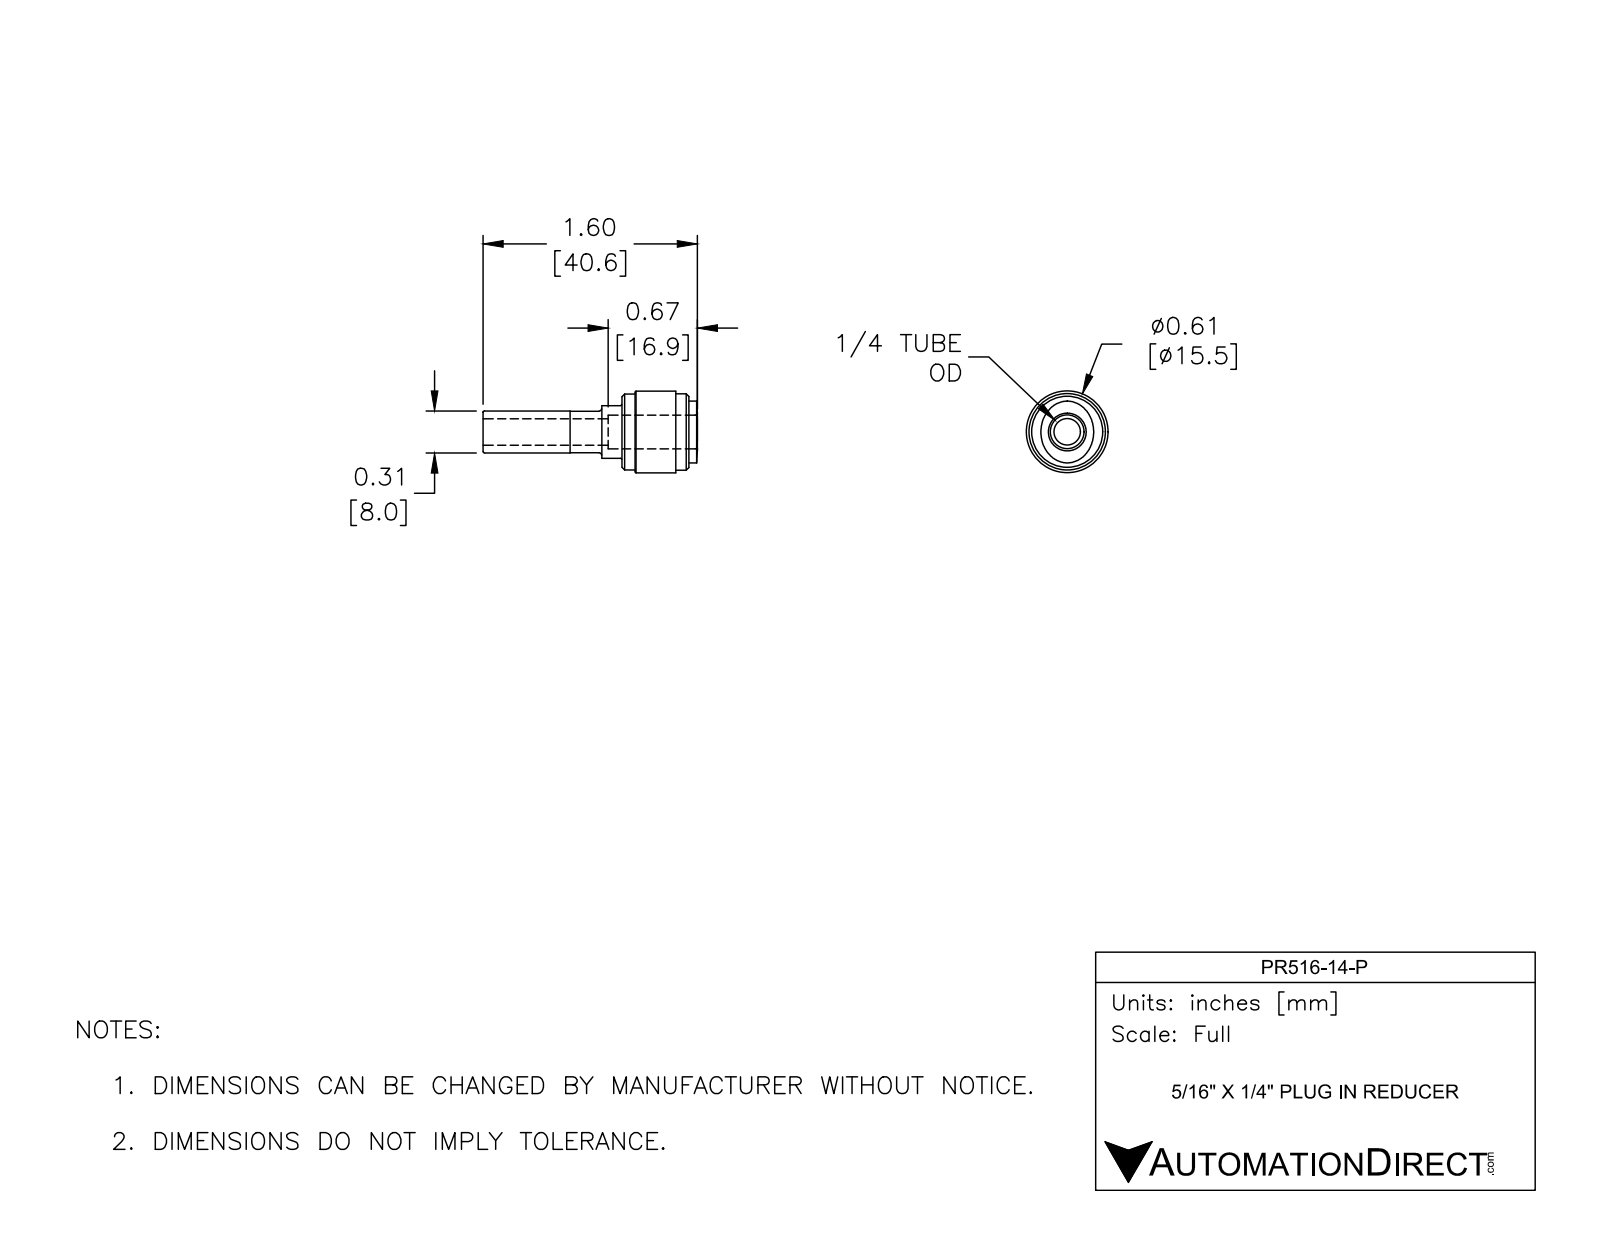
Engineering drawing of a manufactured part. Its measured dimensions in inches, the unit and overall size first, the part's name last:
Units: inches
Overall size (bounding box): 1.598 × 0.61 × 0.61
Round holes (diameter × count): ⌀0.197 ×1, ⌀0.25 ×1
Round bosses / shafts (diameter × count): ⌀0.61 ×1, ⌀0.571 ×1, ⌀0.567 ×1, ⌀0.394 ×1, ⌀0.315 ×1, ⌀0.311 ×1
Main face-to-face distances: 0.5, 0.098, 0.402, 1.035, 1.437, 1.535, 0.65, 0.886, 0.15, 0.551
Volume: 0.172 in³ · Surface area: 3.624 in²
Bodies: 1 solid, 42 faces (8 planar, 16 cylindrical, 18 other)
Part name (STEP PRODUCT): PR516-14-P
STEP written by: SolidWorks 2017 (AUTOMOTIVE_DESIGN)
